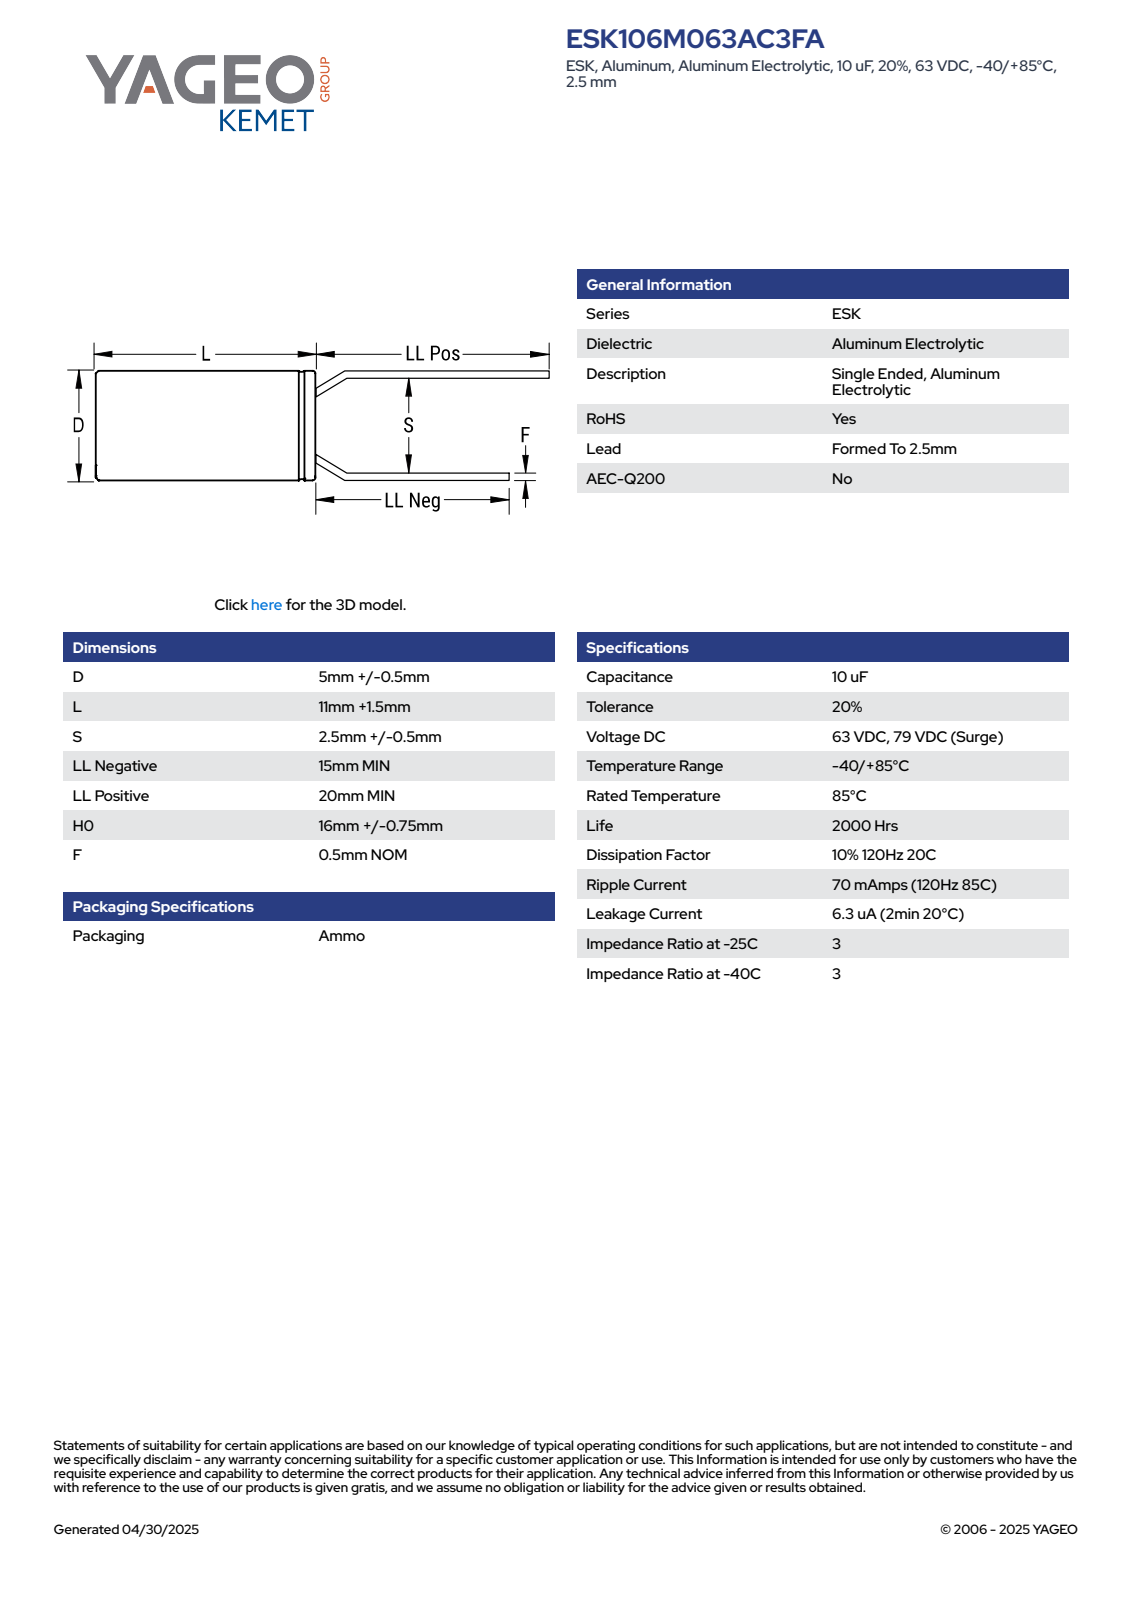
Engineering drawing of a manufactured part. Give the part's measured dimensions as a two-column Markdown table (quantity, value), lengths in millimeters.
| quantity | value |
| --- | --- |
| part name | CAR_KTRF2.5_5X11_D5.5L12.5S2.5F0.5 |
| STEP written by | SolidWorks 2014 (AUTOMOTIVE_DESIGN) |
| units | millimeters |
| bodies | 4 solids, 81 faces (61 planar, 16 cylindrical, 4 other) |
| overall size | 25 × 5.5 × 5.5 |
| volume | 300 mm³ |
| surface area | 312 mm² |
| round bosses / shafts (diameter × count) | 0.5 × 6, 5.5 × 1 |
| main face-to-face distances | 12.5, 12.51, 25.01, 25, 0.65, 0.66, 2.67, 0.4, 1.35, 2.01 |
